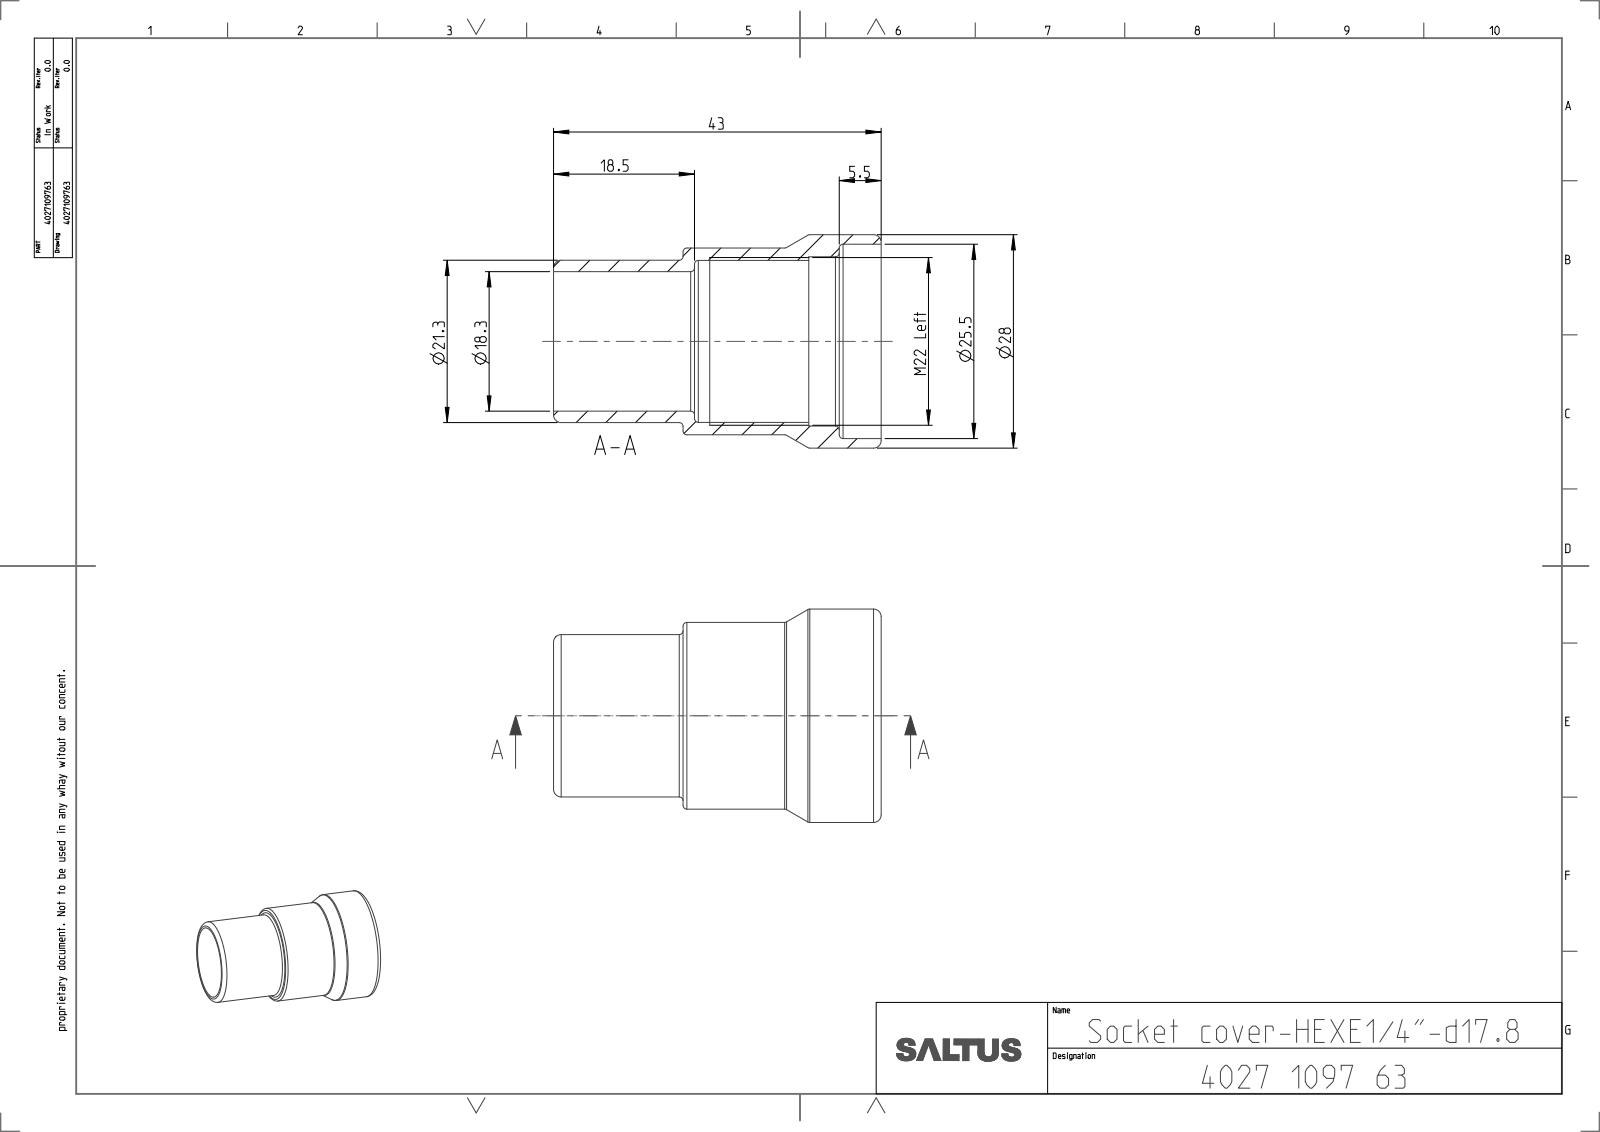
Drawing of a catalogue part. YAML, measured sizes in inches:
part_name: "4027109763"
step_written_by: "CREO PARAMETRIC BY PTC INC, 2022414 (CONFIG_CONTROL_DESIGN)"
units: inches
bodies: {solids: 1, faces: 45, planar: 7, cylindrical: 16, other: 22}
overall_size: [1.693, 1.102, 1.102]
volume: 0.325
surface_area: 11.49
round_holes:
  - {diameter: 0.72, count: 1}
  - {diameter: 0.837, count: 1}
  - {diameter: 0.874, count: 1}
  - {diameter: 1.004, count: 1}
round_bosses_or_shafts:
  - {diameter: 1.102, count: 1}
  - {diameter: 0.965, count: 1}
  - {diameter: 0.866, count: 1}
  - {diameter: 0.839, count: 1}
face_to_face_distances: [0.807, 0.669, 0.157, 0.65, 1.476, 1.319, 0.748, 0.591, 0.059, 0.728]
